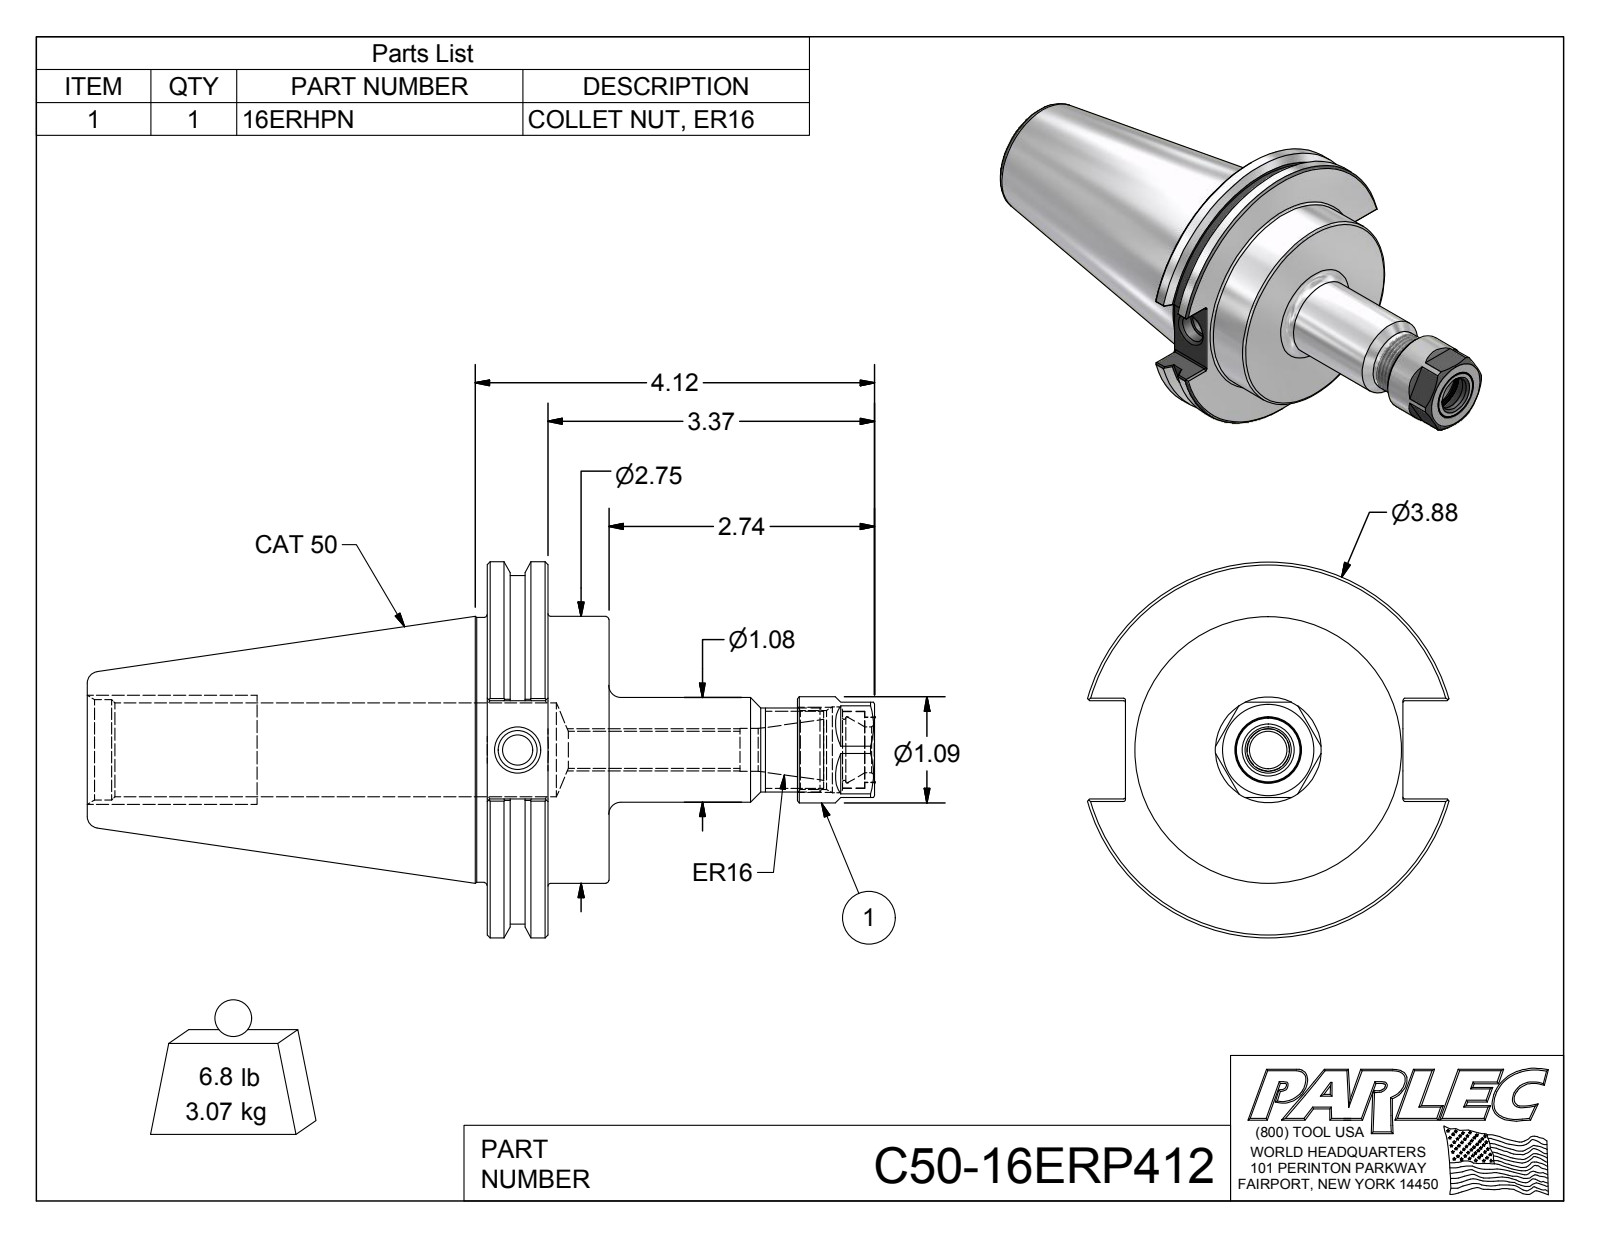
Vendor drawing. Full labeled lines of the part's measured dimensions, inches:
Part name (STEP PRODUCT): C50-16ERP412; C50-16ER4-1; 16ERHPN
STEP written by: Autodesk Inventor 2012 (AUTOMOTIVE_DESIGN)
Units: inches
Bodies: 3 solids, 136 faces (53 planar, 38 cylindrical, 45 other)
Overall size (bounding box): 8.12 × 3.875 × 3.729
Volume: 24.11 in³ · Surface area: 93.67 in²
Round holes (diameter × count): ⌀0.315 ×1, ⌀0.383 ×1, ⌀0.399 ×1, ⌀0.44 ×1, ⌀0.474 ×1, ⌀0.63 ×1, ⌀0.674 ×1, ⌀0.68 ×1, ⌀0.794 ×1, ⌀0.814 ×1, ⌀0.883 ×1, ⌀0.97 ×1
Round bosses / shafts (diameter × count): ⌀3.875 ×1, ⌀3.594 ×1, ⌀2.75 ×1, ⌀2.73 ×1, ⌀1.092 ×1, ⌀1.08 ×1, ⌀0.866 ×1, ⌀0.79 ×1
Partial cylindrical surfaces — rounded edges, fillets, slot ends (radius × count): R0.02 ×12
Main face-to-face distances: 1.255, 0.625, 0.63, 4.125, 4.75, 5.38, 0.98, 8.12, 3.995, 3.37
